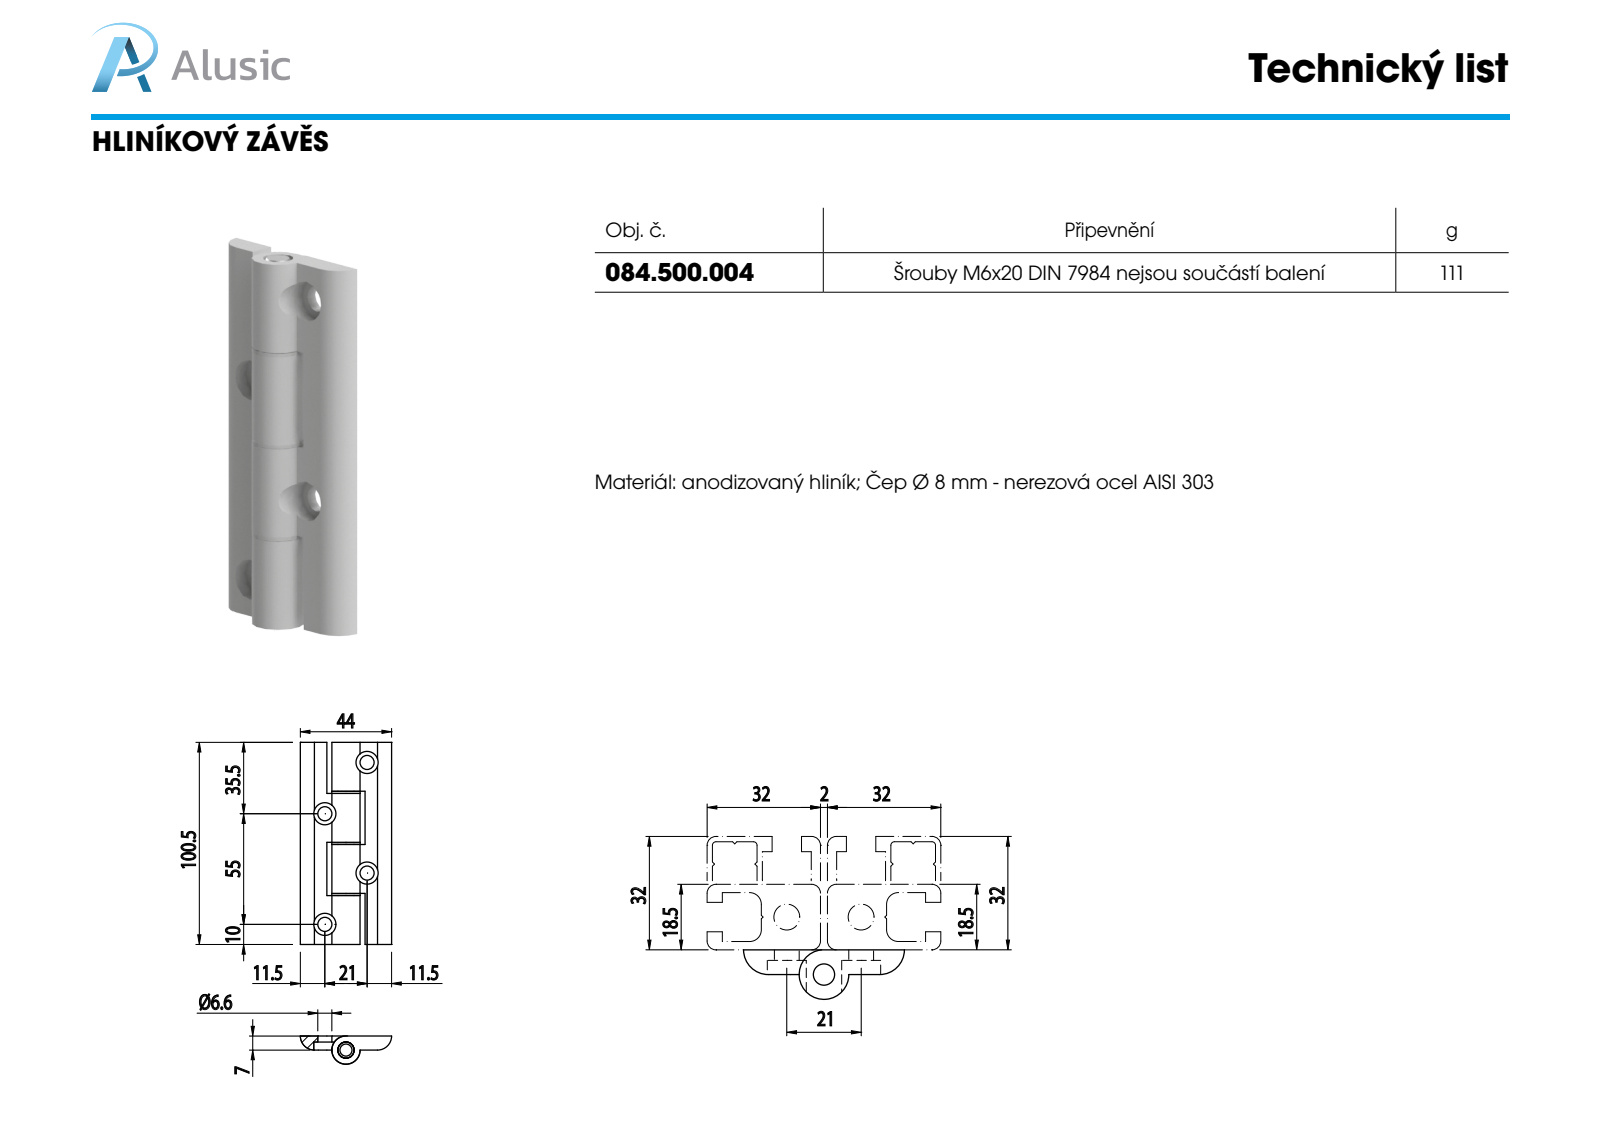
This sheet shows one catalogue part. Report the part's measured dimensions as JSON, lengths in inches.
{"part_name": "084.500.004; 084.500.001.C; PERNO CERNIERA_084.500.004.B; SEMI CERNIERA_084.500.004.A", "step_written_by": "SolidWorks 2011 (CONFIG_CONTROL_DESIGN)", "units": "inches", "bodies": {"solids": 6, "faces": 204, "planar": 154, "cylindrical": 46, "other": 4}, "overall_size": [3.937, 1.171, 0.563], "volume_in3": 1.921, "surface_area_in2": 29.35, "round_holes": [[0.26, 4], [0.433, 4], [0.319, 1], [0.323, 1]], "round_bosses_or_shafts": [[0.555, 1], [0.551, 1], [0.315, 1]], "partial_cylinders_radius": [[0.264, 2]], "face_to_face_distances": [0.264, 0.039, 0.984, 0.955, 2.982, 1.004, 0.994, 2.943, 1.988, 1.939], "hole_center_spacings": [2.165]}
